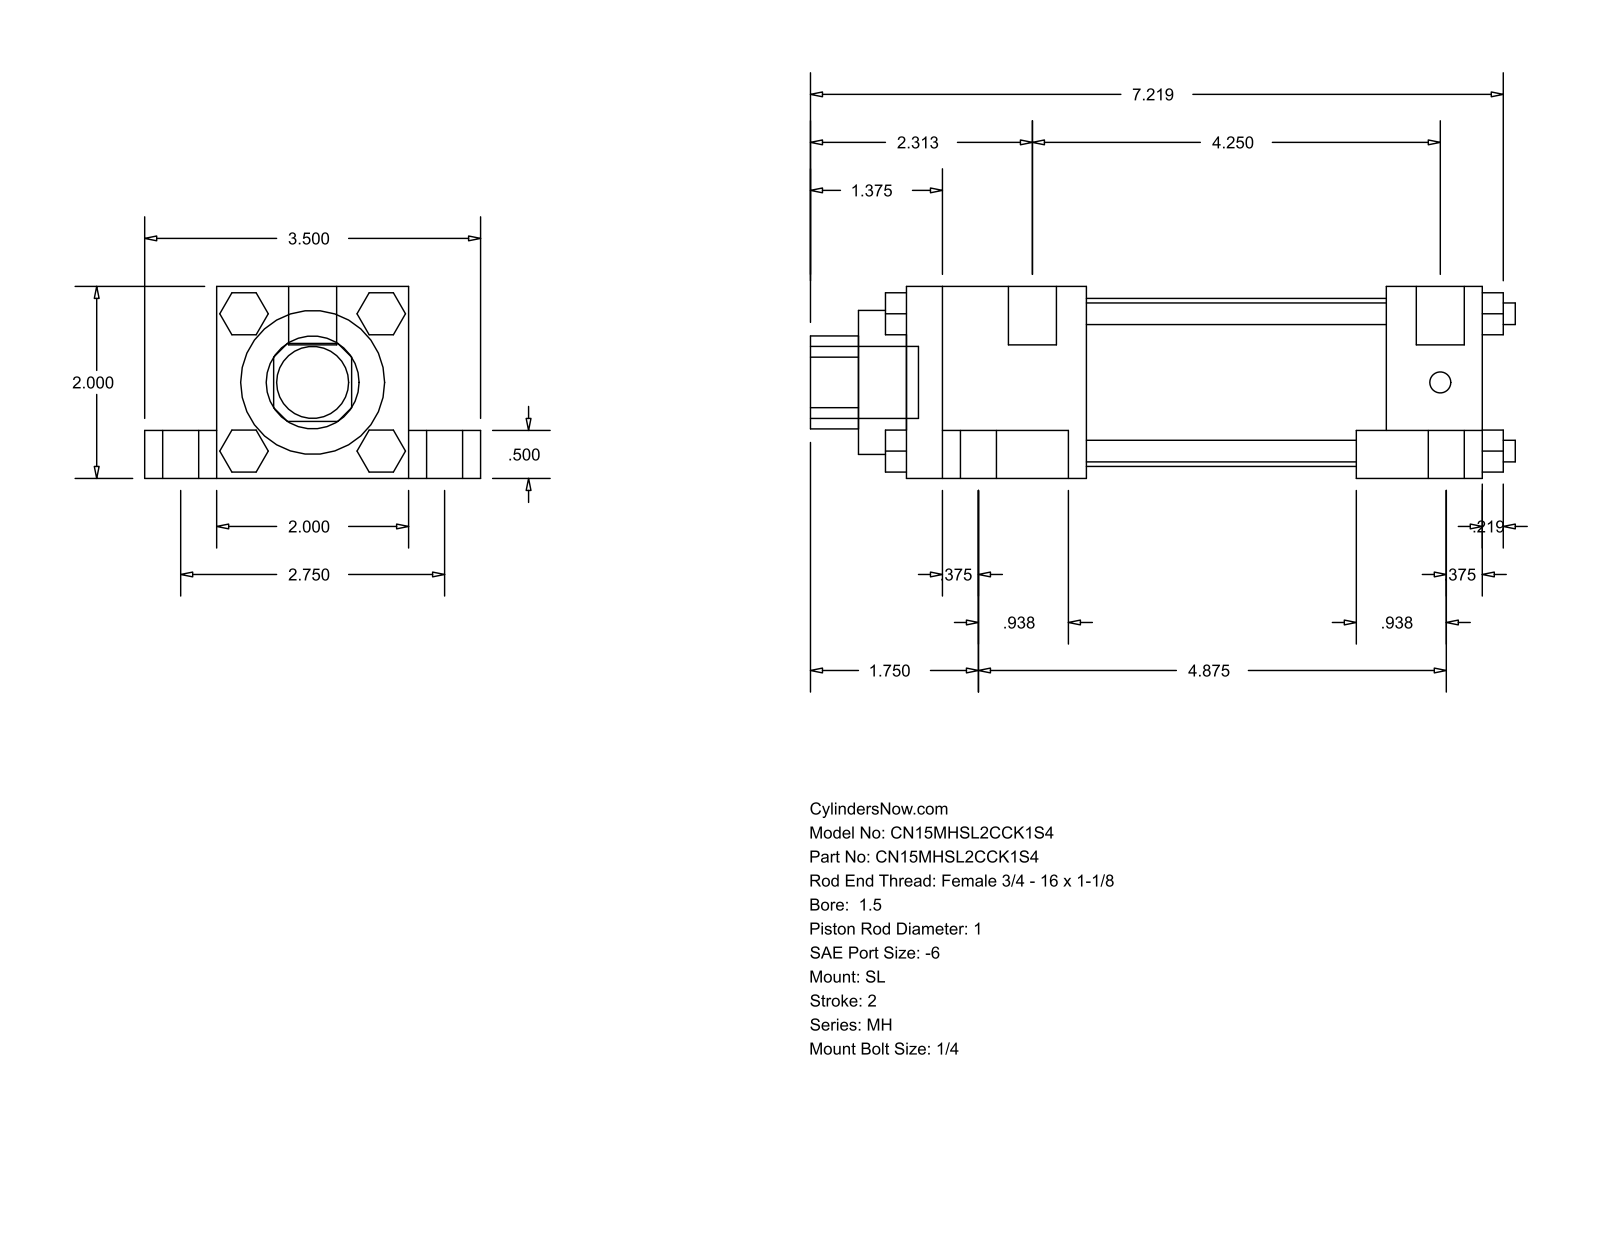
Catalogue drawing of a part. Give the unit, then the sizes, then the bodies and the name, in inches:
Units: inches
Overall size (bounding box): 7.344 × 3.5 × 2
Round holes (diameter × count): ⌀1 ×1, ⌀1.5 ×1, ⌀1.75 ×1
Round bosses / shafts (diameter × count): ⌀0.625 ×4, ⌀0.375 ×4, ⌀0.225 ×4, ⌀0.219 ×4, ⌀0.5 ×2, ⌀0.75 ×1
Partial cylindrical surfaces — rounded edges, fillets, slot ends (radius × count): R0.484 ×1
Main face-to-face distances: 2, 0.5, 1.5, 0.75, 2.75, 6, 1, 0.375, 1.313, 4.313
Bodies: 0 solids, 148 faces (112 planar, 36 cylindrical, 0 other)
Part name (STEP PRODUCT): MH_SL__0150_1
STEP written by: GSSL Pune (CONFIG_CONTROL_DESIGN)
